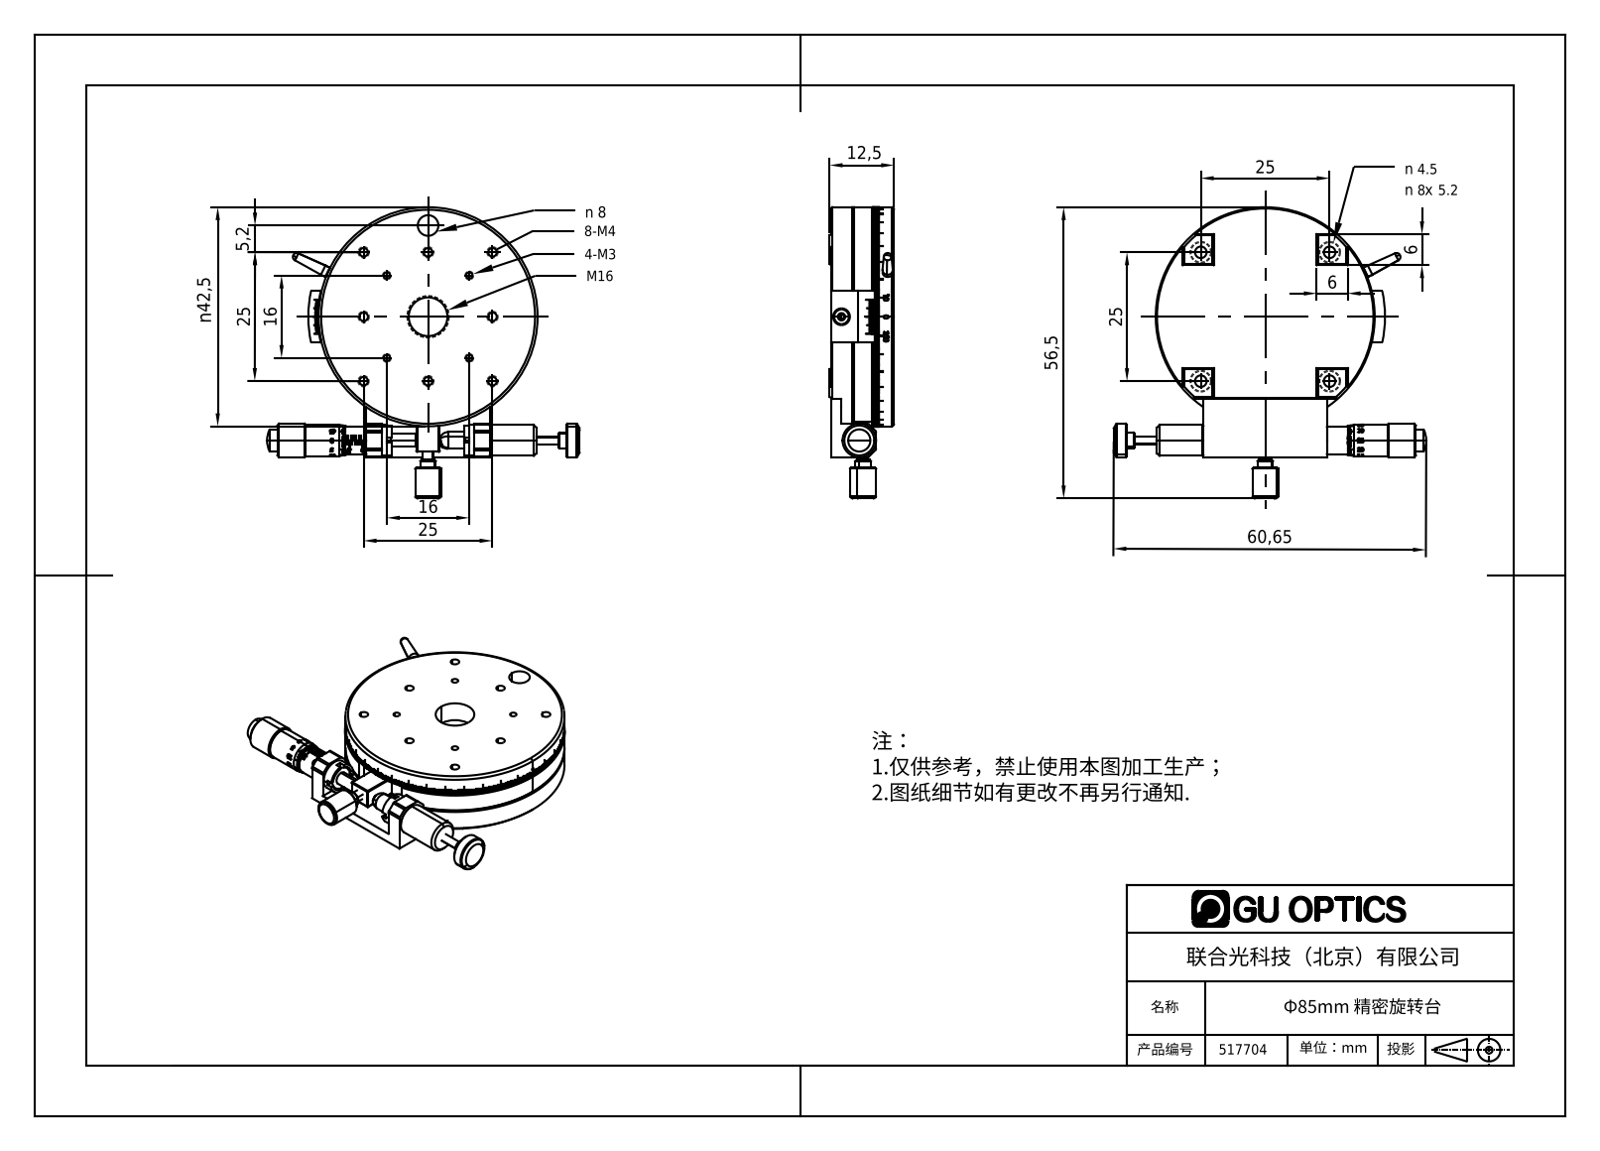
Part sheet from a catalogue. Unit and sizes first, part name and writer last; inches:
Units: inches
Overall size (bounding box): 4.775 × 4.449 × 0.984
Round holes (diameter × count): ⌀0.098 ×9, ⌀0.13 ×9, ⌀0.315 ×5, ⌀0.177 ×4, ⌀0.134 ×1, ⌀0.256 ×1, ⌀0.354 ×1, ⌀0.433 ×1, ⌀0.591 ×1, ⌀2.067 ×1, ⌀2.362 ×1
Round bosses / shafts (diameter × count): ⌀0.024 ×190, ⌀0.118 ×3, ⌀0.236 ×2, ⌀0.157 ×2, ⌀3.346 ×1, ⌀1.181 ×1, ⌀0.512 ×1, ⌀0.476 ×1
Partial cylindrical surfaces — rounded edges, fillets, slot ends (radius × count): R0.039 ×4, R0.216 ×1, R0.238 ×1, R1.673 ×1, R1.679 ×1, R1.831 ×1
Main face-to-face distances: 0.335, 0.315, 0.65, 0.02, 0.63, 0.965, 0.669, 0.295, 0.157, 0.354
Hole centre spacings: 0.984, 0.649, 0.723, 1.092, 1.109, 1.27, 1.392, 1.653
Volume: 7.739 in³ · Surface area: 78.26 in²
Bodies: 16 solids, 3420 faces (1972 planar, 615 cylindrical, 833 other)
Part name (STEP PRODUCT): MR85-AR
STEP written by: SolidWorks 2020 (CONFIG_CONTROL_DESIGN)
